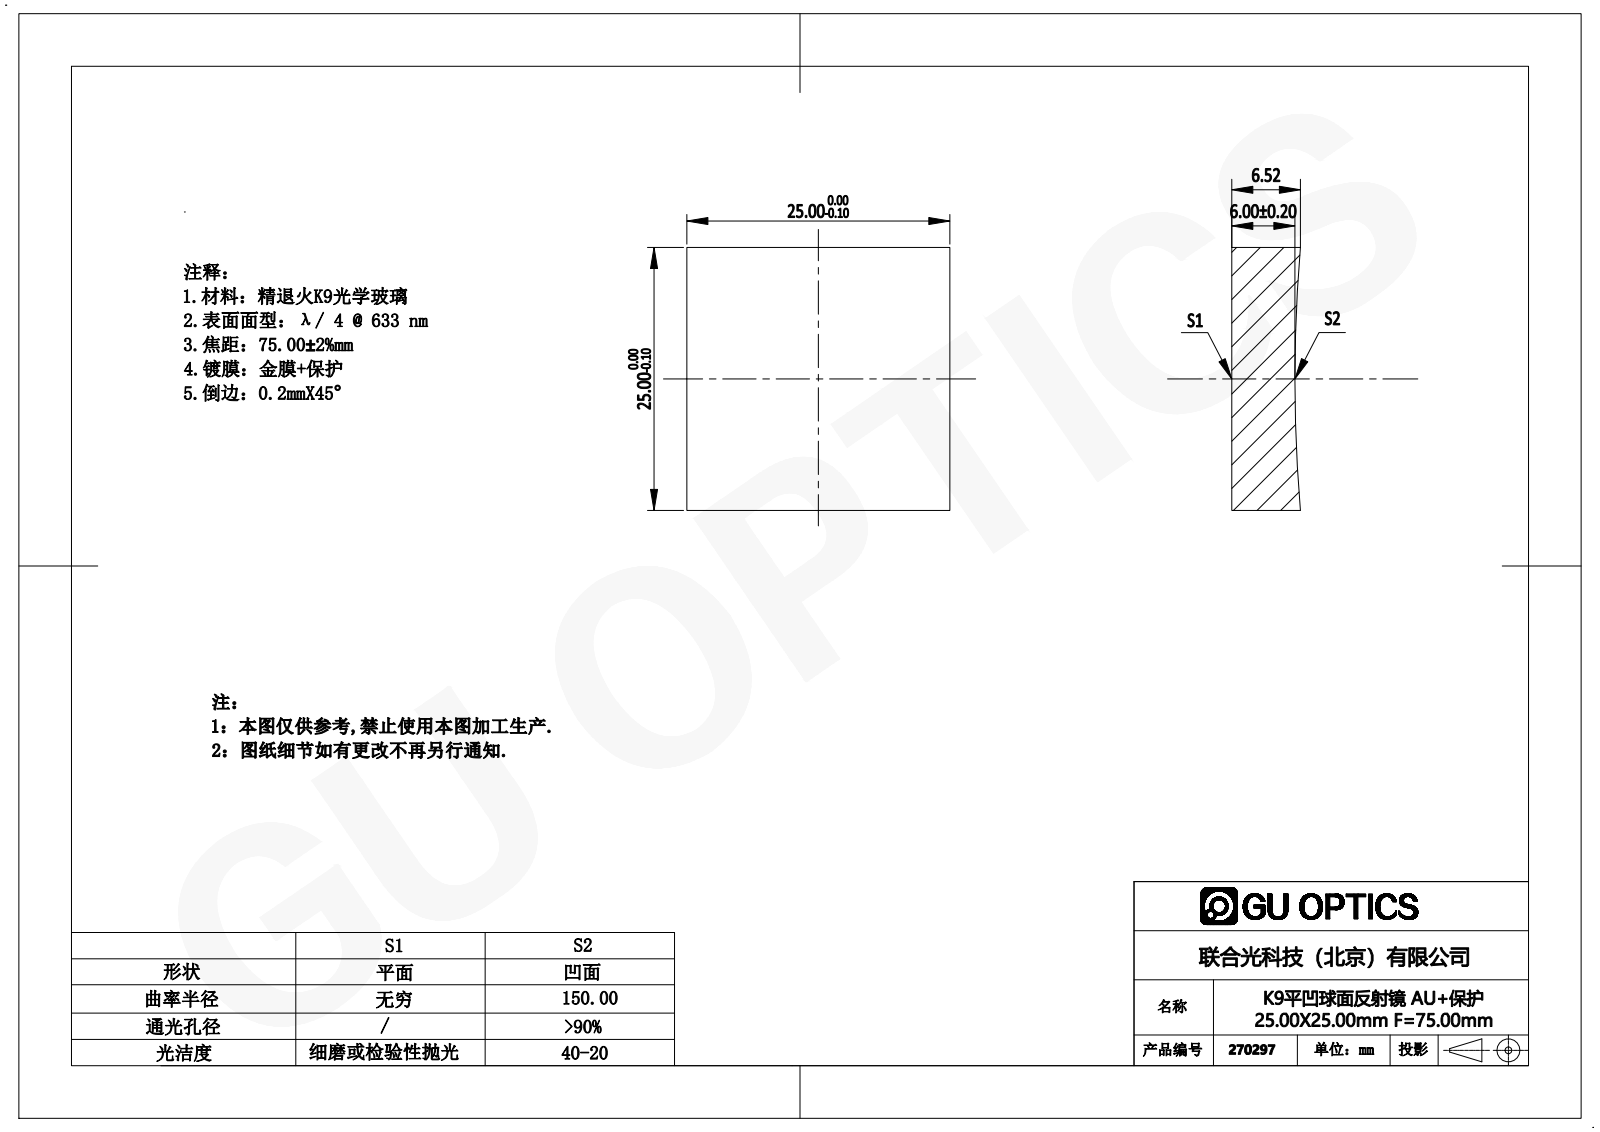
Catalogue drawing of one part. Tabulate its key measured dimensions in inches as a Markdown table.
| quantity | value |
| --- | --- |
| part name | 270037 |
| STEP written by | SolidWorks 2016 (AUTOMOTIVE_DESIGN) |
| units | inches |
| bodies | 1 solid, 7 faces (5 planar, 2 cylindrical, 0 other) |
| overall size | 0.984 × 0.984 × 0.257 |
| volume | 0.235 in³ |
| surface area | 2.923 in² |
| partial cylindrical surfaces (radius × count) | 5.906 × 1 |
| main face-to-face distances | 0.984 |
